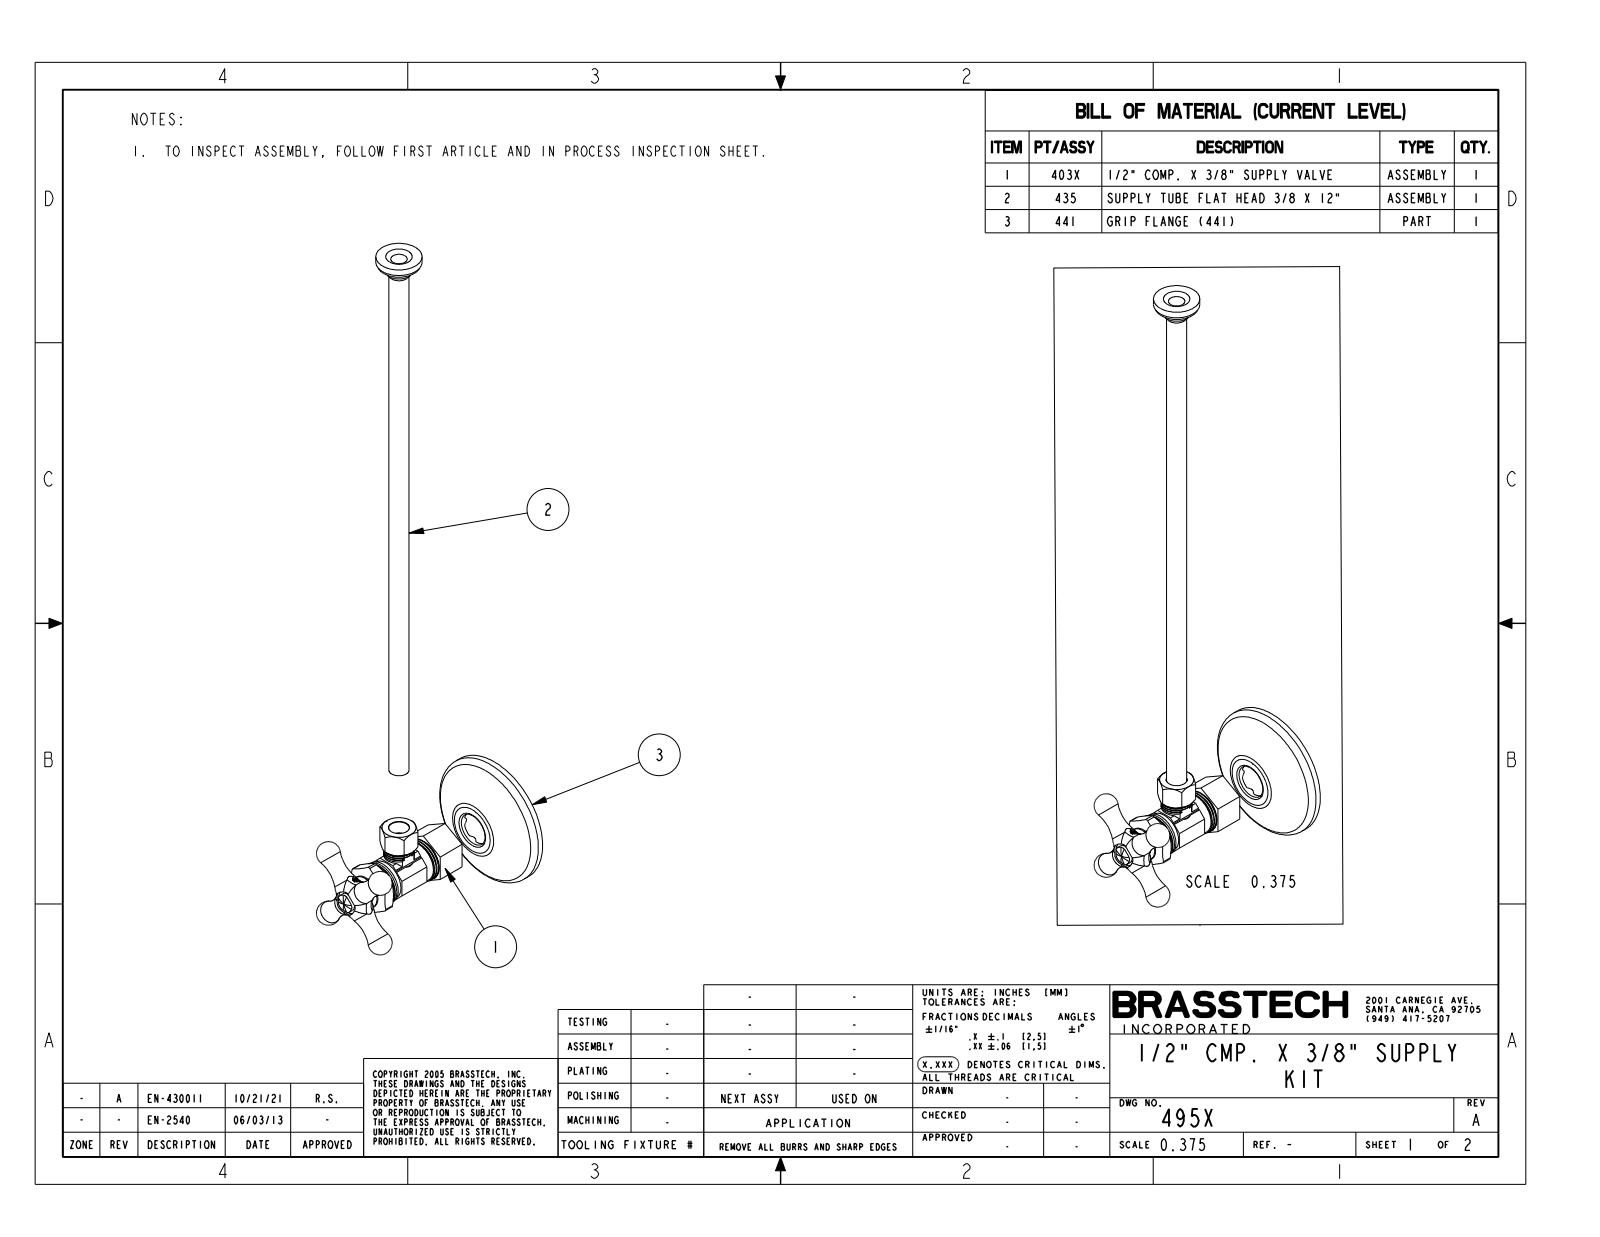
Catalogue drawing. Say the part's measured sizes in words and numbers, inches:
The part is named "495X". Its 3-D file was written by "CREO PARAMETRIC BY PTC INC, 2018500 (CONFIG_CONTROL_DESIGN)". It is 5 solids with 743 faces: 189 planar, 256 cylindrical and 298 other. Overall it measures 13.055 by 3.894 by 2.5 inches. Its volume is 1.315 cubic inches and its surface area 100.4 square inches. Round holes: 1 of diameter 0.13, 1 of diameter 0.32, 1 of diameter 0.375, 1 of diameter 0.38, 1 of diameter 0.392, 1 of diameter 0.4, 1 of diameter 0.45, 1 of diameter 0.464, 1 of diameter 0.48, 1 of diameter 0.563, 1 of diameter 0.625, 1 of diameter 0.75. Round bosses or shafts: 1 of diameter 2.5, 1 of diameter 0.86, 1 of diameter 0.845, 1 of diameter 0.753, 1 of diameter 0.68, 1 of diameter 0.677, 1 of diameter 0.663, 1 of diameter 0.629. Partial cylindrical surfaces (rounded edges, fillets, slot ends): 18 of radius 0.01, 10 of radius 0.03, 6 of radius 0.05, 5 of radius 0.058, 1 of radius 0.17, 1 of radius 0.376. The main face-to-face distances are 0.875, 0.625, 0.1, 0.125, 0.75, 0.8, 0.563, 0.463, 0.037, 0.837. The hole center spacings are 1.09.
